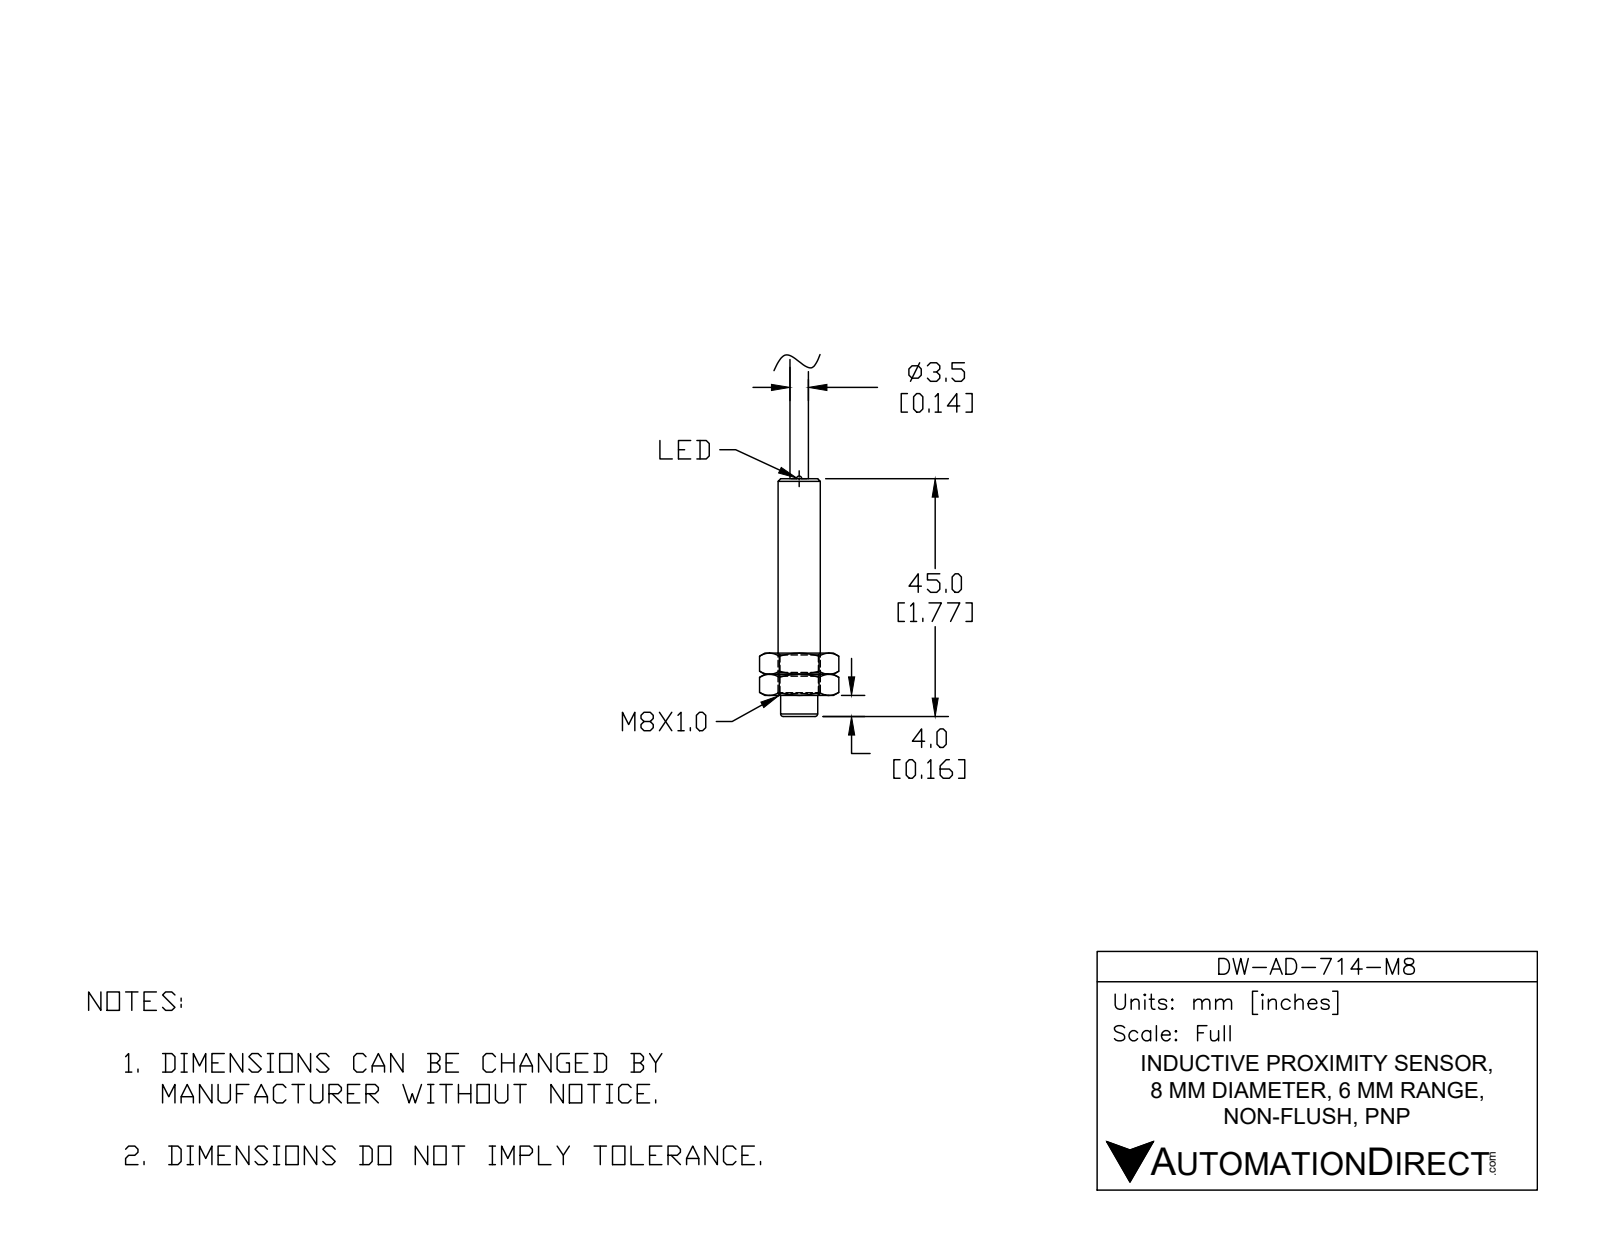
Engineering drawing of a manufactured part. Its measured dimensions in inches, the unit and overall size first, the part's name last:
Units: inches
Overall size (bounding box): 2.559 × 0.315 × 0.315
Round bosses / shafts (diameter × count): ⌀0.315 ×1, ⌀0.276 ×1, ⌀0.138 ×1
Main face-to-face distances: 1.772, 0.787, 2.559
Volume: 0.147 in³ · Surface area: 2.236 in²
Bodies: 2 solids, 9 faces (4 planar, 3 cylindrical, 2 other)
Part name (STEP PRODUCT): DW-AD-714-M8
STEP written by: SolidWorks 2017 (AUTOMOTIVE_DESIGN)
